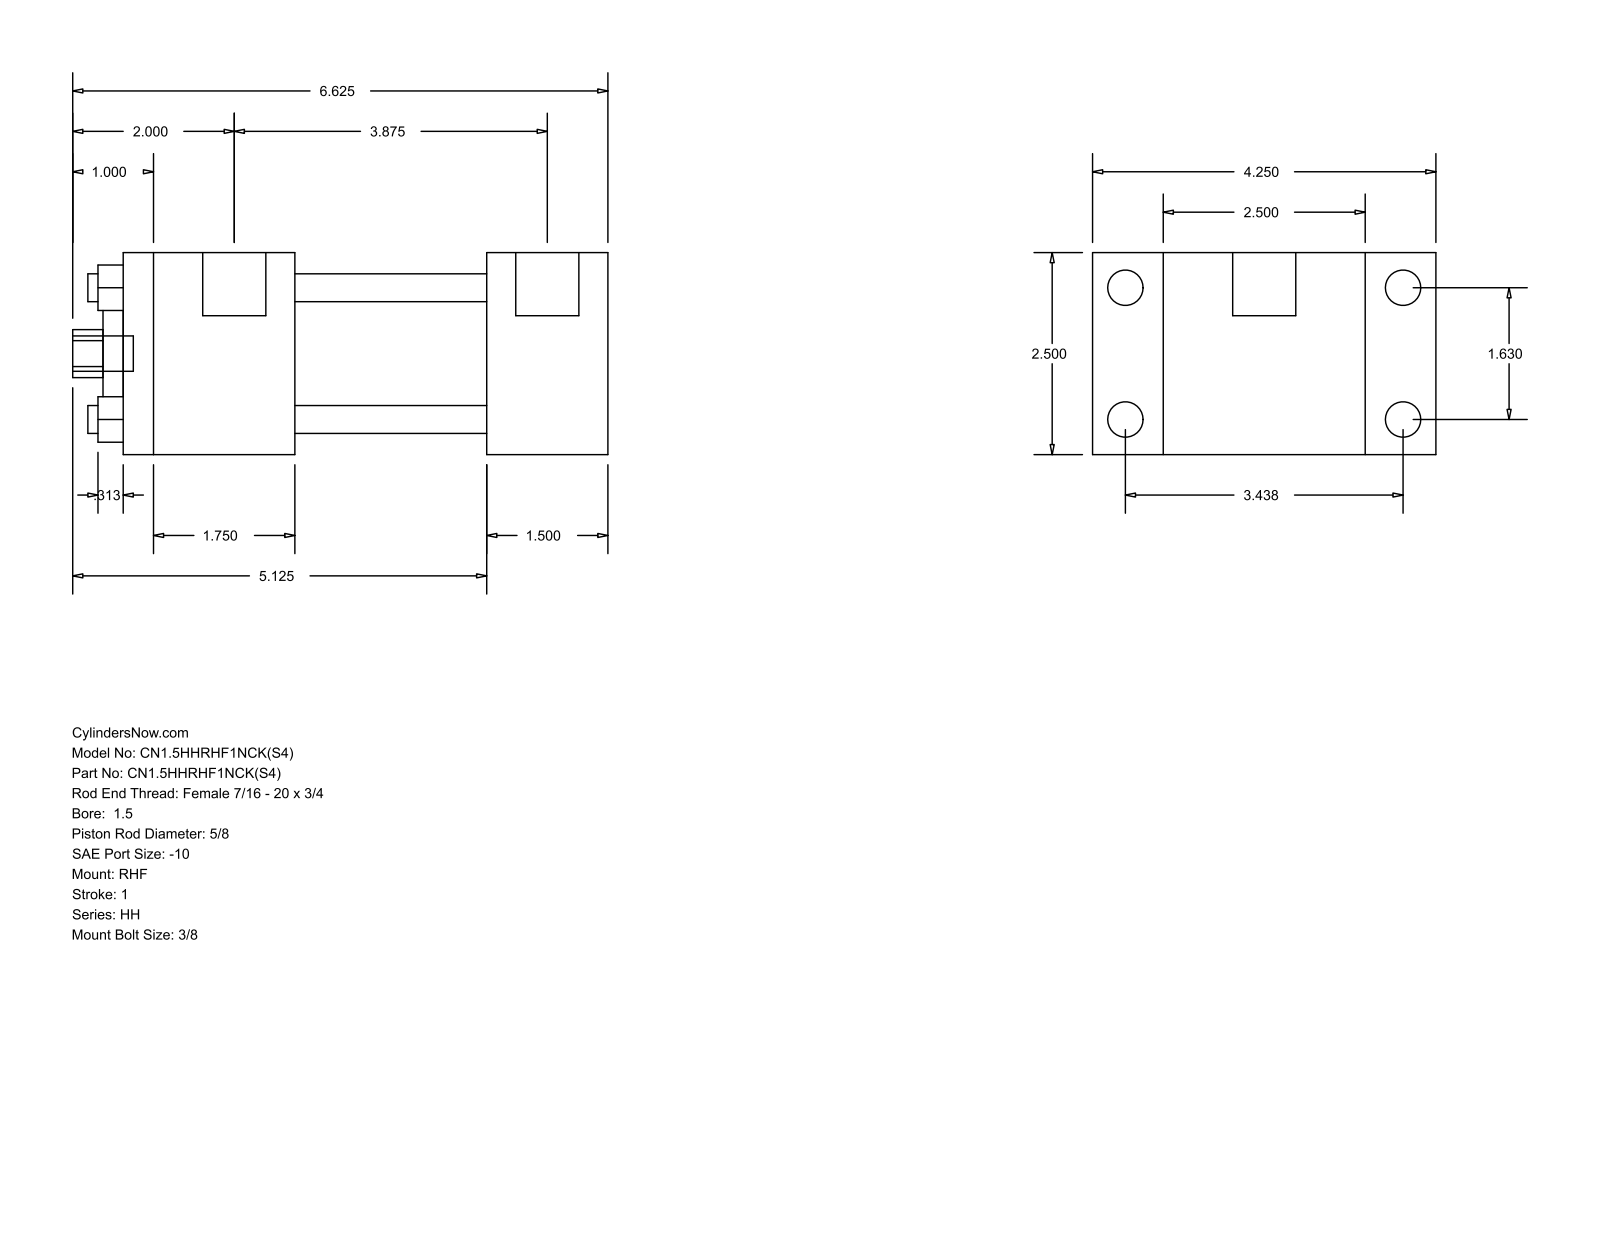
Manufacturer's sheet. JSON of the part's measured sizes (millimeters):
{"part_name": "HH_RHF__0150_0.625", "step_written_by": "GSSL Pune (CONFIG_CONTROL_DESIGN)", "units": "millimeters", "bodies": {"solids": 0, "faces": 88, "planar": 60, "cylindrical": 28, "other": 0}, "overall_size": [168.28, 107.95, 63.5], "round_holes": [[8.76, 4], [15.88, 1], [28.57, 1], [44.45, 1]], "round_bosses_or_shafts": [[11.13, 4], [5.56, 4], [19.84, 2], [11.11, 1]], "partial_cylinders_radius": [[7.54, 1]], "face_to_face_distances": [63.5, 38.1, 22.23, 85.73, 114.3, 152.4, 107.96, 60.33, 53.97, 98.43], "hole_center_spacings": [29.27, 41.4, 58.55]}
